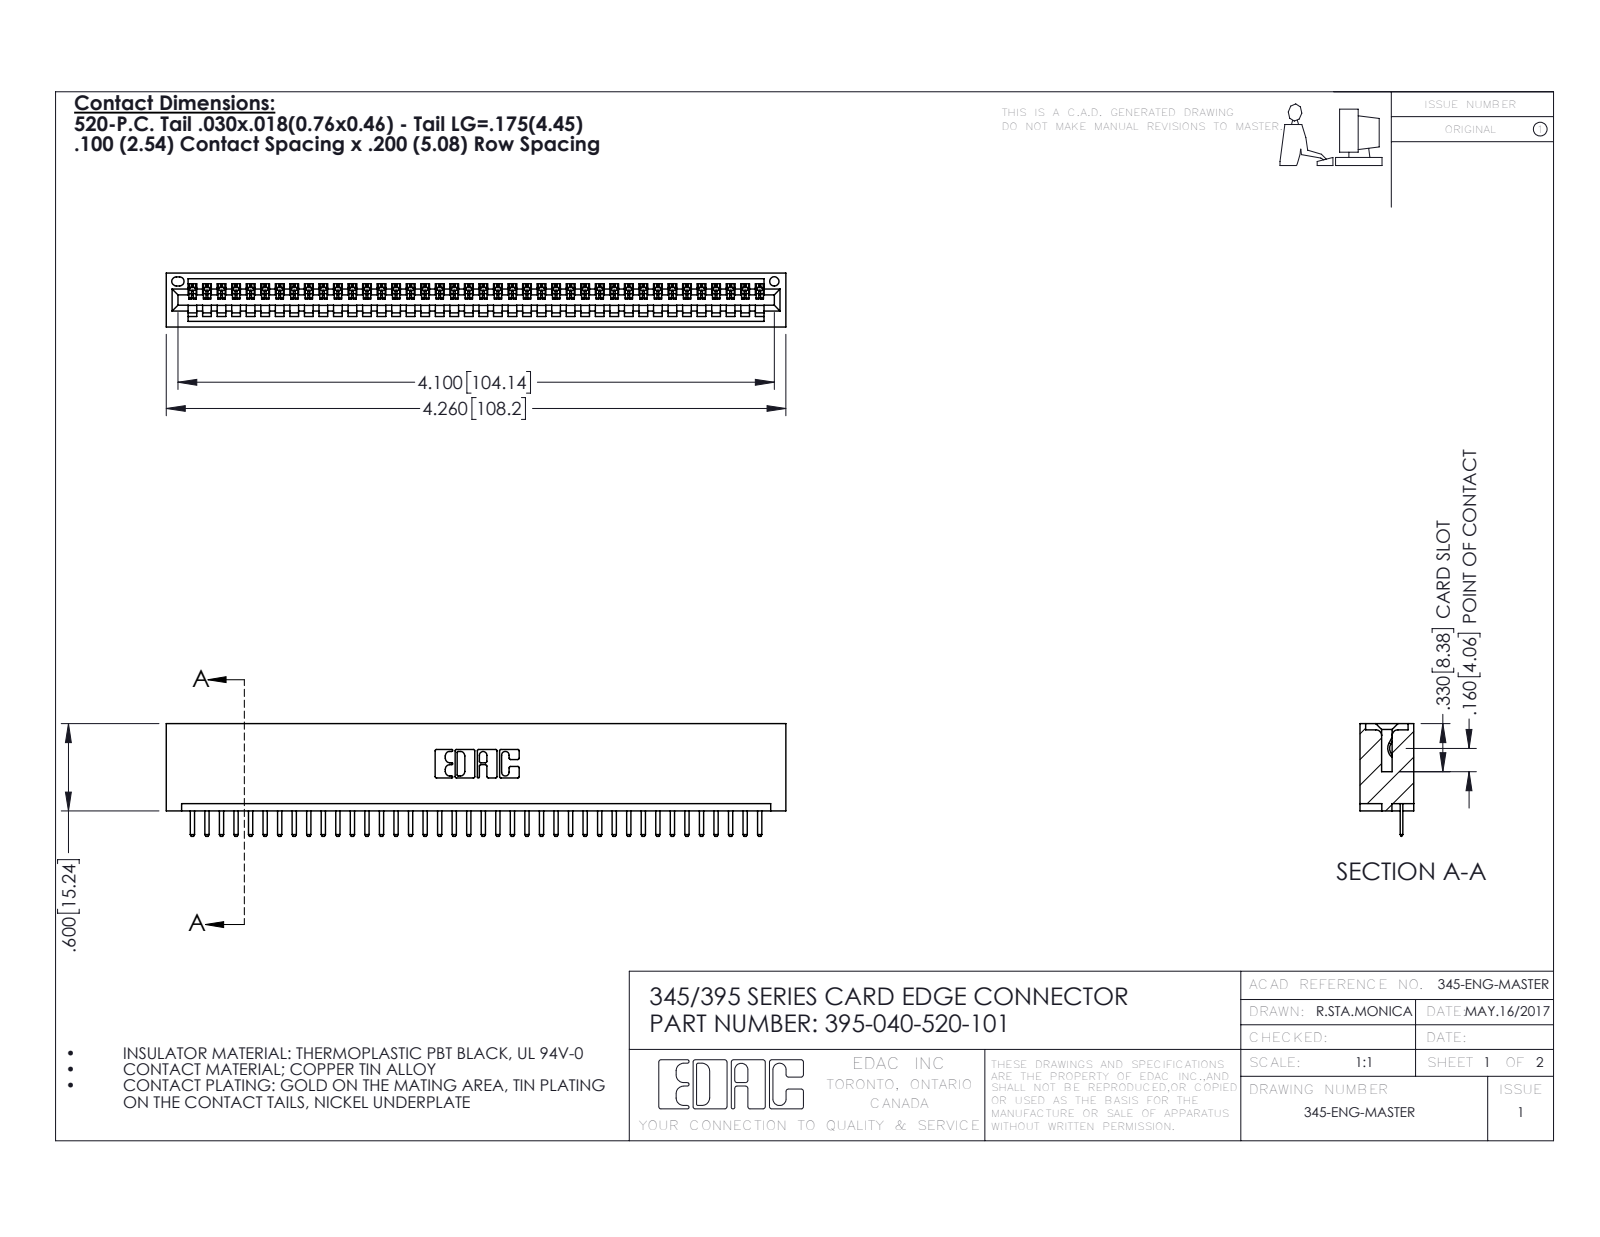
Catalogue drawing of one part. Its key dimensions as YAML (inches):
part_name: "345-292-001_345-293-120; 345 Part_No Mounting Lugs; 395-040-520-101"
step_written_by: "SolidWorks 2016 (CONFIG_CONTROL_DESIGN)"
units: inches
bodies: {solids: 41, faces: 2598, planar: 1756, cylindrical: 842, other: 0}
overall_size: [4.26, 0.775, 0.37]
volume: 0.655
surface_area: 21.77
round_holes:
  - {diameter: 0.064, count: 1}
partial_cylinders:
  - {radius: 0.01, count: 82}
  - {radius: 0.006, count: 80}
  - {radius: 0.01, count: 22}
  - {radius: 0.007, count: 6}
  - {radius: 0.031, count: 6}
  - {radius: 0.026, count: 3}
  - {radius: 0.031, count: 2}
  - {radius: 0.04, count: 2}
face_to_face_distances: [0.298, 0.072, 0.37, 0.2, 0.098, 0.272, 0.025, 0.225, 0.072, 0.149]
